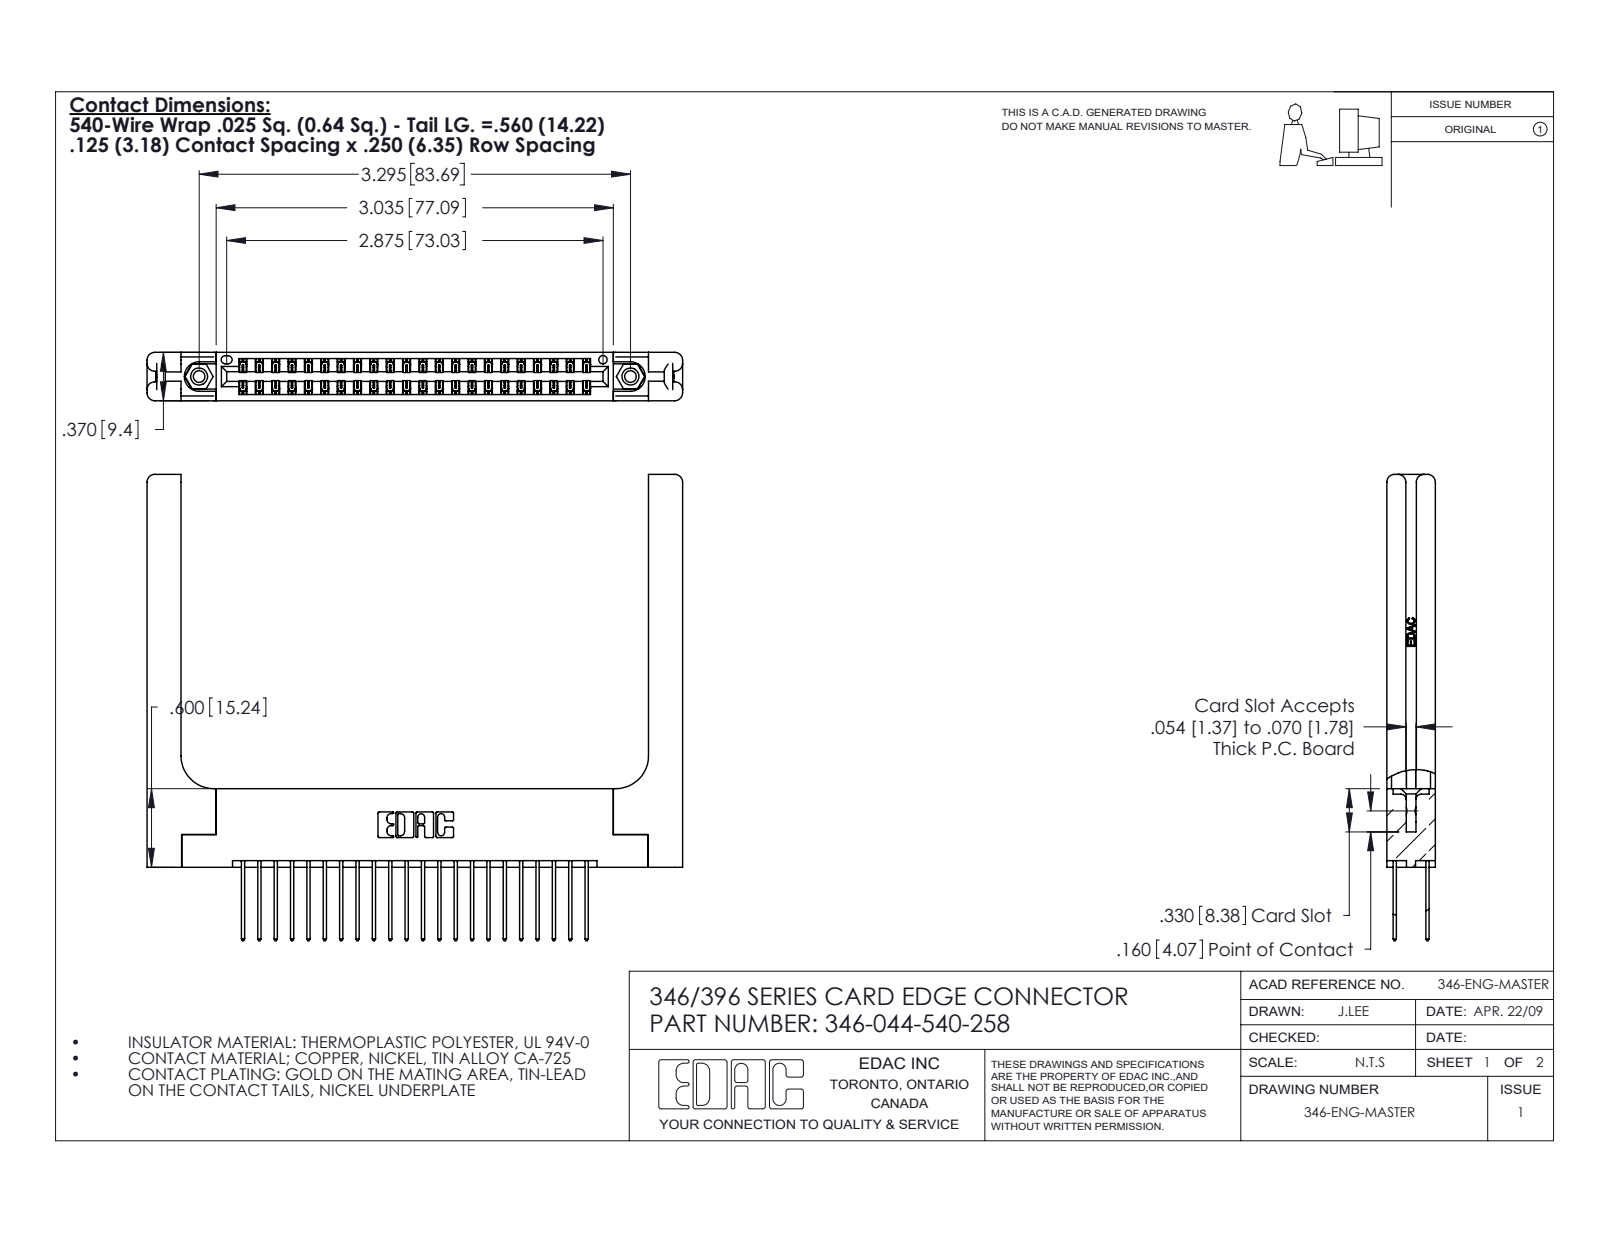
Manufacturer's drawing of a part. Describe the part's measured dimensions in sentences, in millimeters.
The part is named "345-250-001_345-250-001-102; 345-292-001_345-293-140; 346 Part_Flush Mounting Lugs - 0.156 Dia-TH; 346-044-540-258 (+1 more)". Its 3-D file was written by "SolidWorks 2020 (CONFIG_CONTROL_DESIGN)". It is 49 solids with 2680 faces: 1778 planar, 842 cylindrical and 60 other. Overall it measures 103.9 by 90.4 by 9.4 millimeters. Its volume is 17 620 cubic millimeters and its surface area 19 400 square millimeters. Round holes: 2 of diameter 2.3, 2 of diameter 3.2, 2 of diameter 4, 1 of diameter 1.6. Round bosses or shafts: 2 of diameter 3.9. Partial cylindrical surfaces (rounded edges, fillets, slot ends): 66 of radius 0.2, 44 of radius 0.3, 22 of radius 0.3, 16 of radius 1.5, 6 of radius 0.2, 6 of radius 0.8, 3 of radius 0.7, 2 of radius 0.4. The main face-to-face distances are 9.4, 1.8, 1.2, 8.2, 6.4, 3.8, 3.8, 0.6, 7.6, 7. The hole center spacings are 6.2, 78.4, 83.7.
